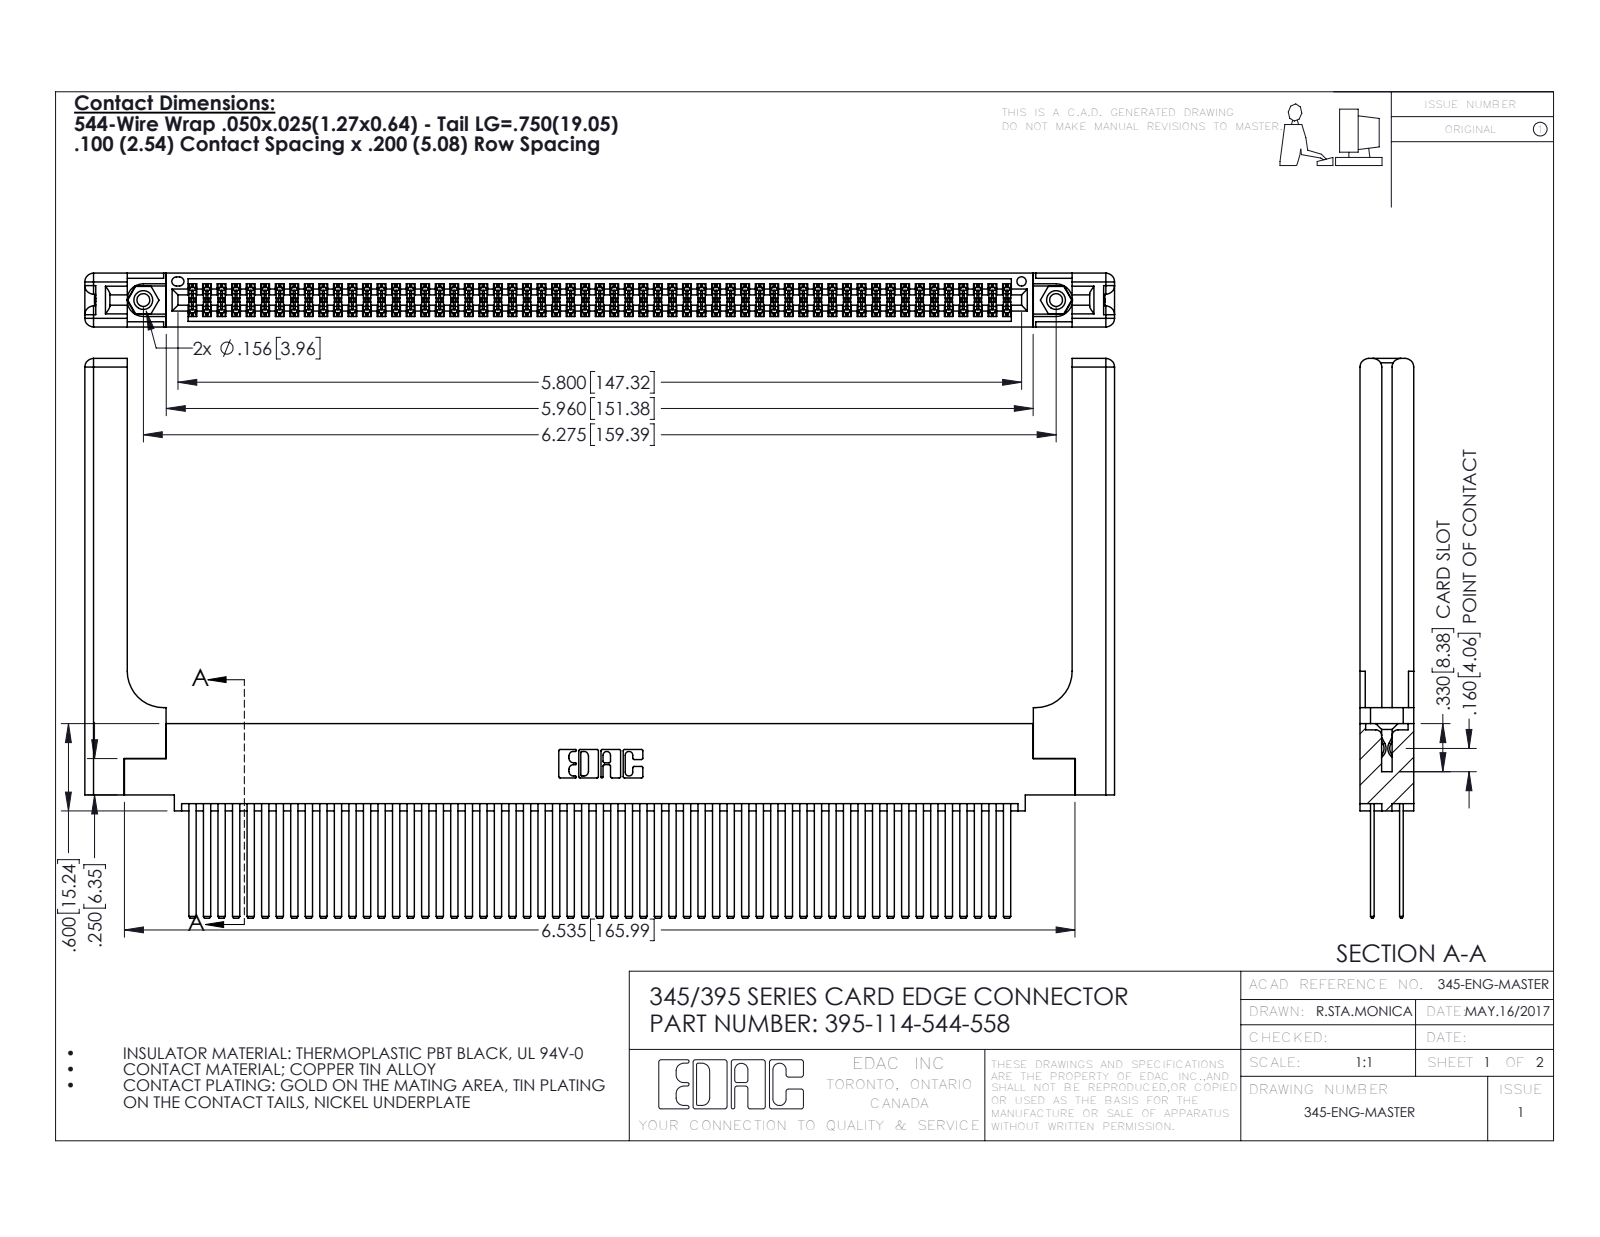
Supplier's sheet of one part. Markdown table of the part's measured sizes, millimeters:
| quantity | value |
| --- | --- |
| part name | 395-114-544-558; 345-292-001_345-293-144; 345-220-058_345-220-058; 345-250-001_345-250-001-102 (+1 more) |
| STEP written by | SolidWorks 2016 (CONFIG_CONTROL_DESIGN) |
| units | millimeters |
| bodies | 119 solids, 5402 faces (3538 planar, 1804 cylindrical, 60 other) |
| overall size | 179.8 × 97.7 × 9.4 |
| volume | 27 610 mm³ |
| surface area | 38 410 mm² |
| round holes (diameter × count) | 2.3 × 2, 3.2 × 2, 4 × 2, 1.6 × 1 |
| round bosses / shafts (diameter × count) | 3.9 × 2 |
| partial cylindrical surfaces (radius × count) | 0.2 × 171, 0.3 × 22, 1.5 × 16, 0.2 × 6, 0.8 × 6, 0.7 × 3, 0.4 × 2, 0.5 × 2 |
| main face-to-face distances | 1.8, 7.6, 2.5, 6.9, 0.6, 5.1, 5.7, 9.4, 4.4, 3.8 |
| hole center spacings | 6.9, 153.4, 159.4 |
